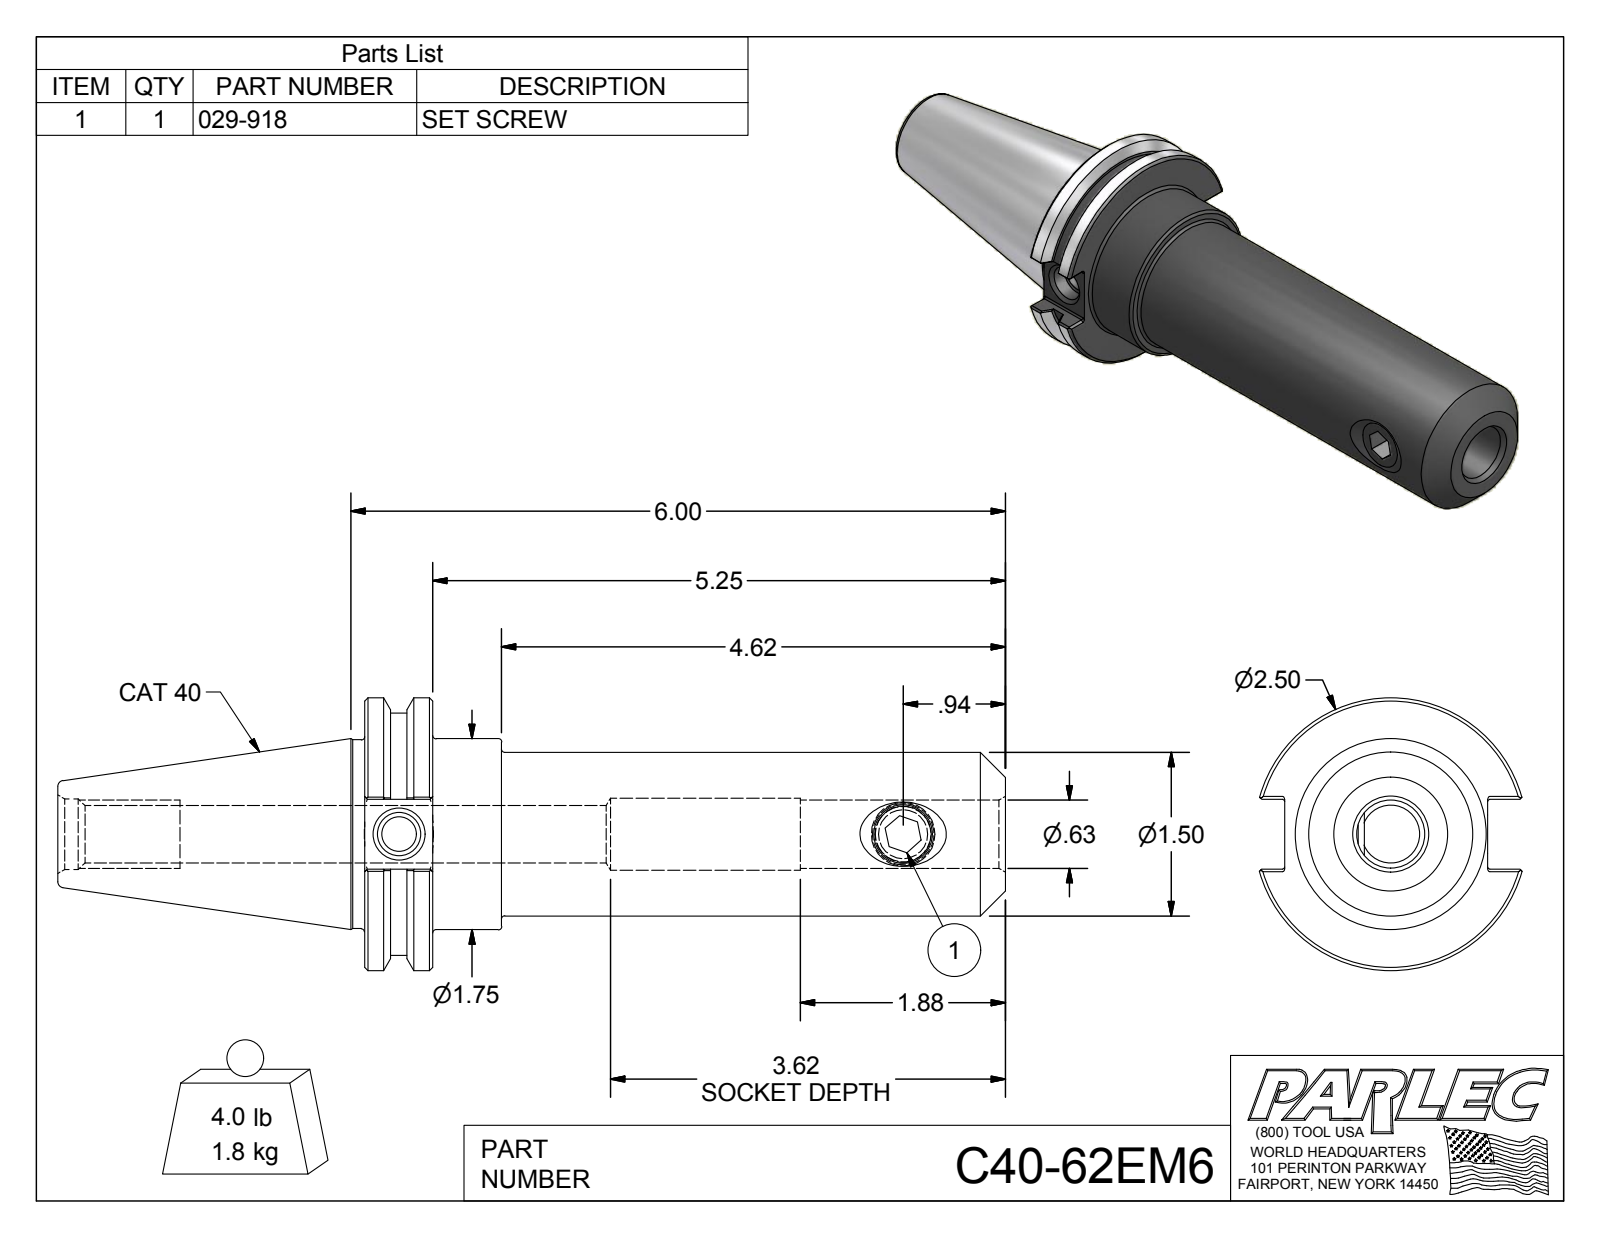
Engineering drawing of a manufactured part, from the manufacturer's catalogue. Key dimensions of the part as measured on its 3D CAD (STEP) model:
Part name (STEP PRODUCT): C40-62EM6; C40-62EM6-1; 029-918
STEP written by: Autodesk Inventor 2012 (AUTOMOTIVE_DESIGN)
Units: inches
Bodies: 2 solids, 104 faces (42 planar, 29 cylindrical, 33 other)
Overall size (bounding box): 8.687 × 2.5 × 2.406
Volume: 14.14 in³ · Surface area: 67.42 in²
Round holes (diameter × count): ⌀0.315 ×1, ⌀0.399 ×1, ⌀0.516 ×1, ⌀0.527 ×1, ⌀0.625 ×1, ⌀0.648 ×1, ⌀0.66 ×1
Round bosses / shafts (diameter × count): ⌀2.5 ×1, ⌀2.219 ×1, ⌀1.75 ×1, ⌀1.73 ×1, ⌀1.5 ×1, ⌀0.563 ×1
Partial cylindrical surfaces — rounded edges, fillets, slot ends (radius × count): R0.02 ×12
Main face-to-face distances: 0.625, 5.875, 5.25, 1.255, 0.63, 4.62, 0.64, 1.86, 0.3, 2.812
Hole centre spacings: 4.622
